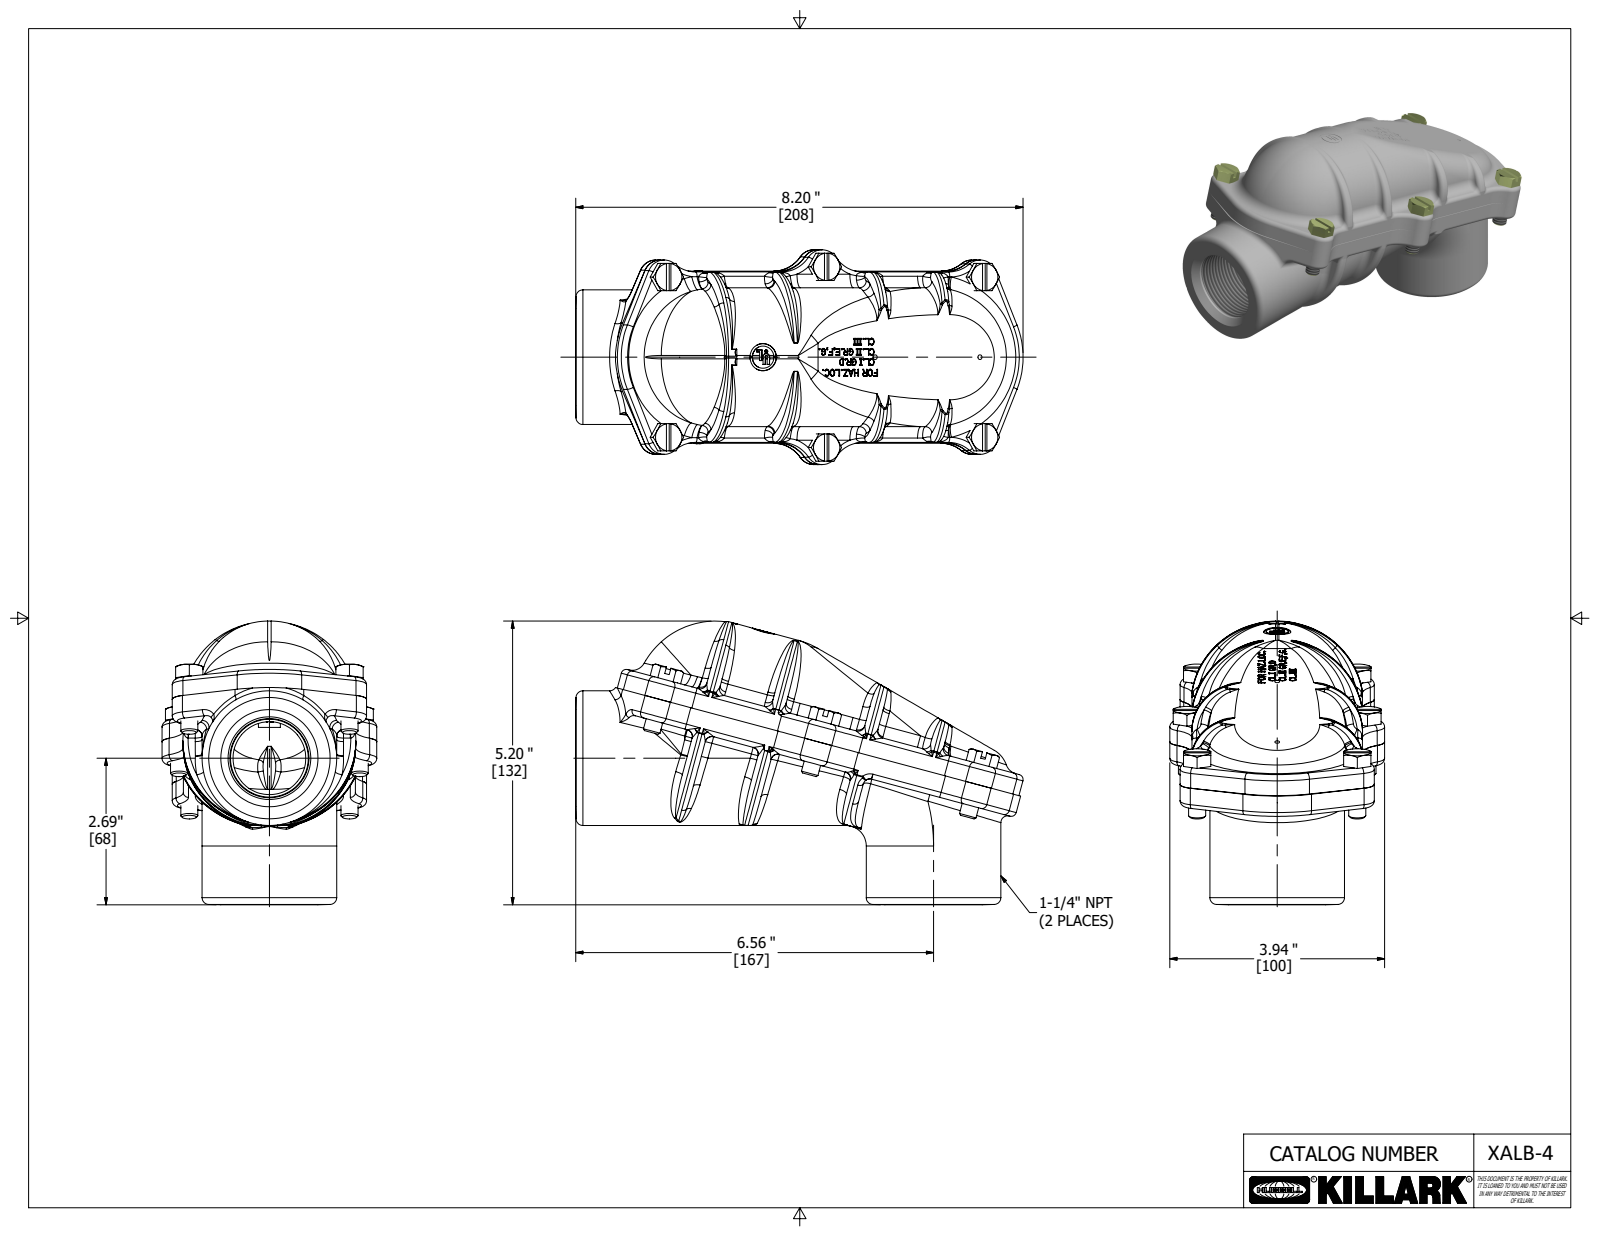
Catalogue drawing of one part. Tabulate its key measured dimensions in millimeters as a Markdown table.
| quantity | value |
| --- | --- |
| part name | XALB-4; 0240370-2; 0240371-2; 0723912B |
| STEP written by | Autodesk Inventor 2020 (AUTOMOTIVE_DESIGN) |
| units | millimeters |
| bodies | 8 solids, 3184 faces (951 planar, 214 cylindrical, 2019 other) |
| overall size | 208.4 × 132.1 × 100 |
| volume | 443 400 mm³ |
| surface area | 130 700 mm² |
| round holes (diameter × count) | 6.4 × 6, 8.7 × 6, 2.2 × 2, 1.4 × 1 |
| round bosses / shafts (diameter × count) | 8 × 6, 62.7 × 2, 1.2 × 1 |
| partial cylindrical surfaces (radius × count) | 2.4 × 41, 3.2 × 18, 15.9 × 16, 39.7 × 14, 8 × 10, 6.4 × 7, 3.2 × 6, 2.4 × 5 |
| main face-to-face distances | 5.6, 54, 12.7, 10.3, 10.3, 67.1, 13.1, 0.4, 79.8, 66.7 |
| hole center spacings | 74.6, 76.4, 110, 76.3, 76.4, 84.2, 110, 152.4 |
